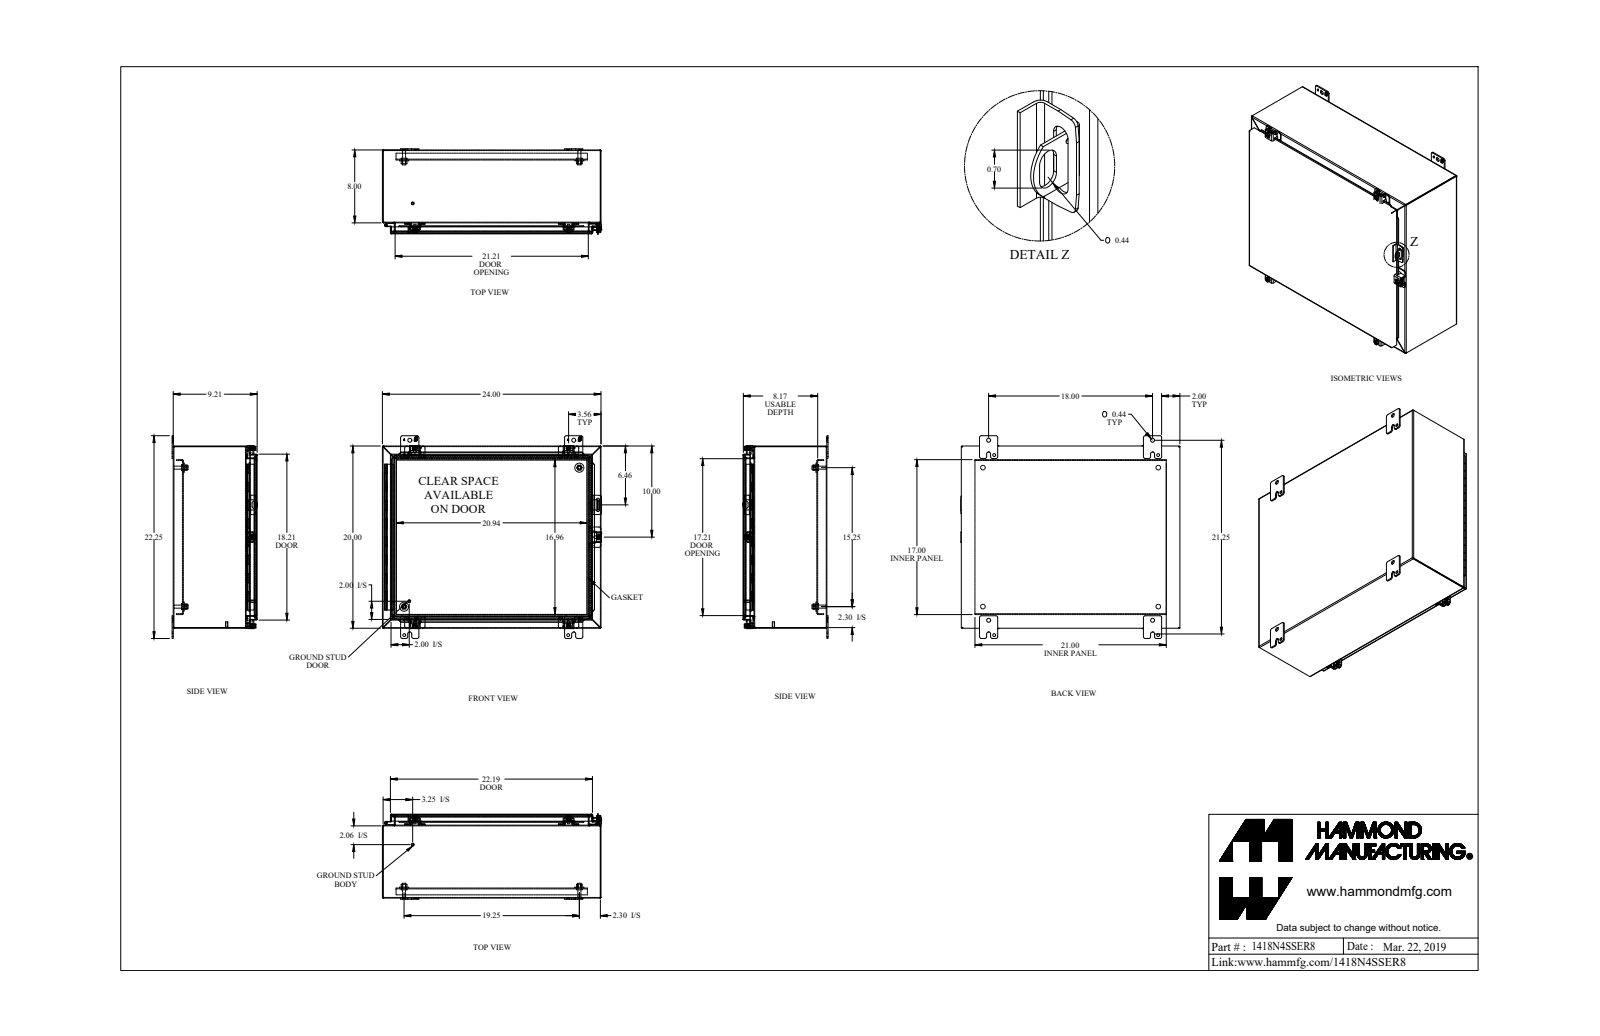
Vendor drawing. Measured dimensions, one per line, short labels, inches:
name: 1418N4SSER8_Default
written by: SolidWorks 2019 (CONFIG_CONTROL_DESIGN)
unit: in
bodies: 43 solids, 1597 faces (997 planar, 506 cylindrical, 94 other)
size: 24.063 × 22.25 × 9.375
volume: 184.6 in³; area: 4 860 in²
holes: 5× ⌀0.213, 5× ⌀0.375, 4× ⌀0.265, 4× ⌀0.313, 4× ⌀0.437, 4× ⌀0.5, 2× ⌀0.307, 2× ⌀0.445, 1× ⌀0.125, 1× ⌀0.187, 1× ⌀0.265
bosses: 5× ⌀0.5, 5× ⌀0.39, 5× ⌀0.244, 4× ⌀0.65, 4× ⌀0.375, 4× ⌀0.332, 2× ⌀1, 2× ⌀0.313
rounds: 26× R0.188, 24× R0.036, 24× R0.108, 24× R0.25, 21× R0.048, 21× R0.143, 10× R0.125, 10× R0.141
face distances: 0.072, 9.066, 9.138, 0.072, 9.138, 9.21, 0.095, 0.937, 19.928, 1.009
hole spacings: 2.434, 3.065, 17.416, 18, 18.187, 24.559, 26.722, 15.25
